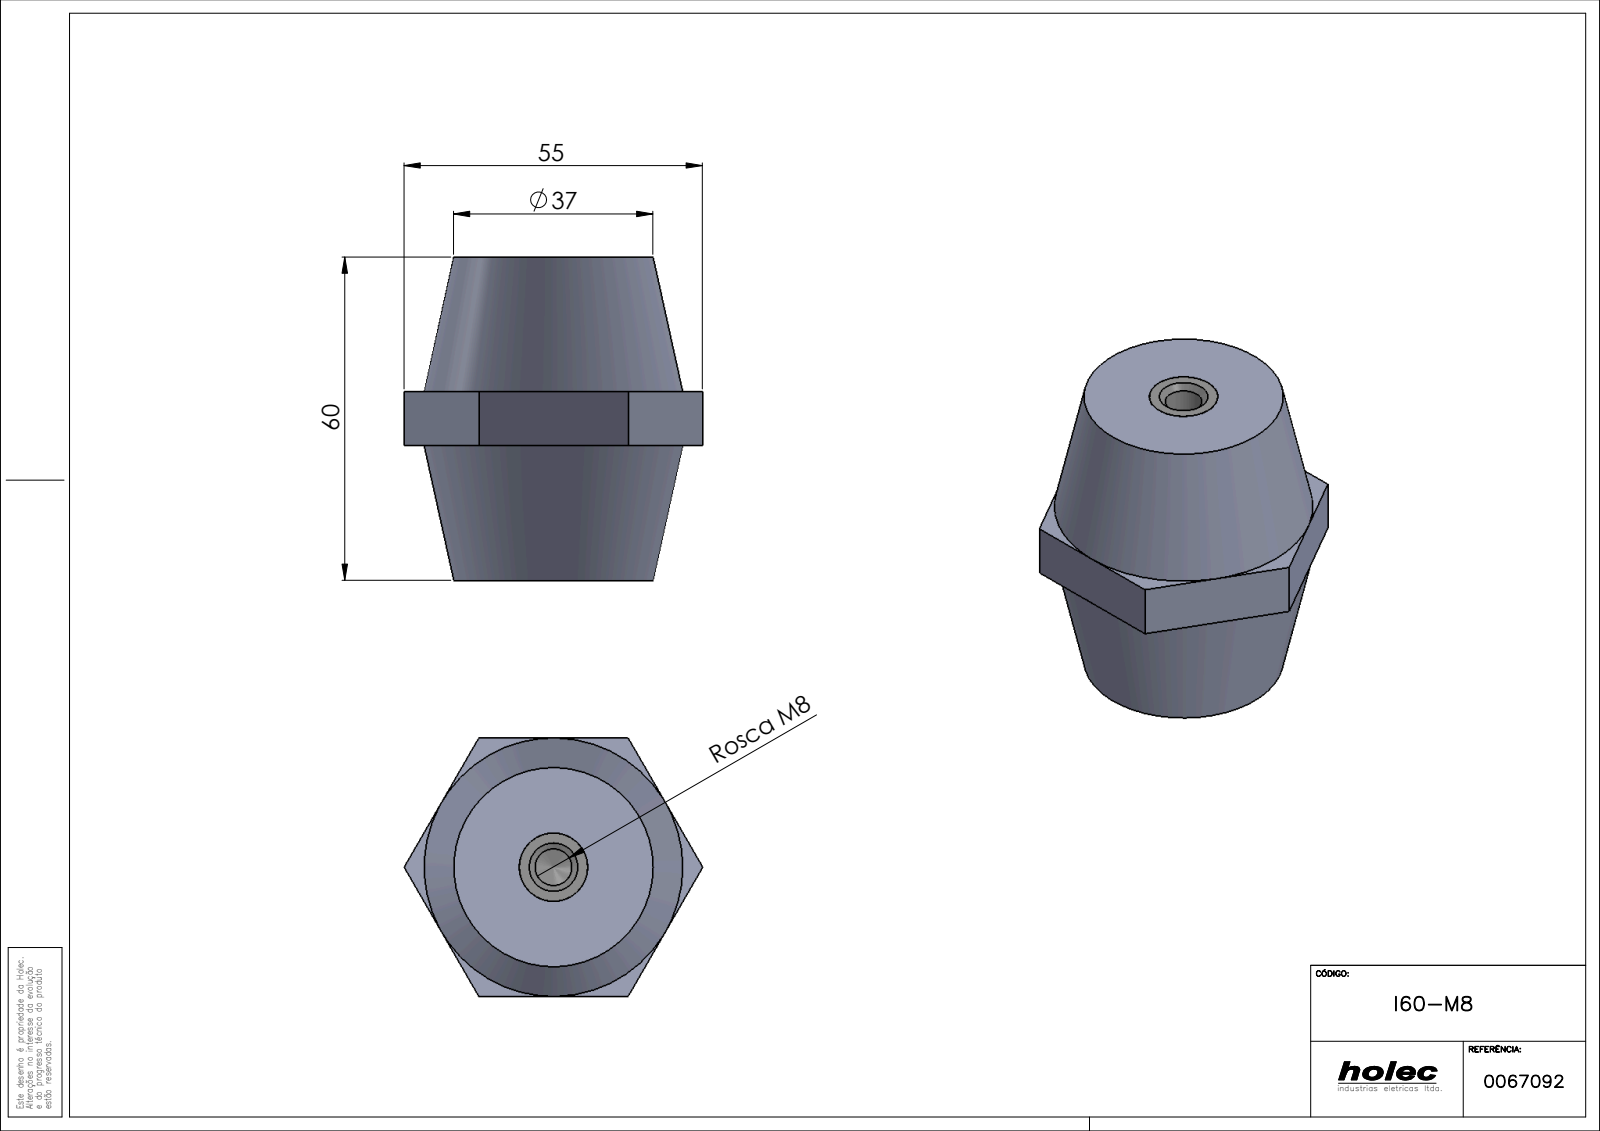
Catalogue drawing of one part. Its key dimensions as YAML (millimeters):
part_name: "I60-M8; PB1_0108(PB1_0108_08); PB1_0005"
step_written_by: "SolidWorks 2017 (AUTOMOTIVE_DESIGN)"
units: millimeters
bodies: {solids: 3, faces: 154, planar: 82, cylindrical: 12, other: 60}
overall_size: [60, 55.43, 48]
volume: 90370
surface_area: 14784
round_holes:
  - {diameter: 6.8, count: 1}
  - {diameter: 10, count: 1}
face_to_face_distances: [60, 48, 12.7, 46, 14, 5, 9, 25, 35, 11]
